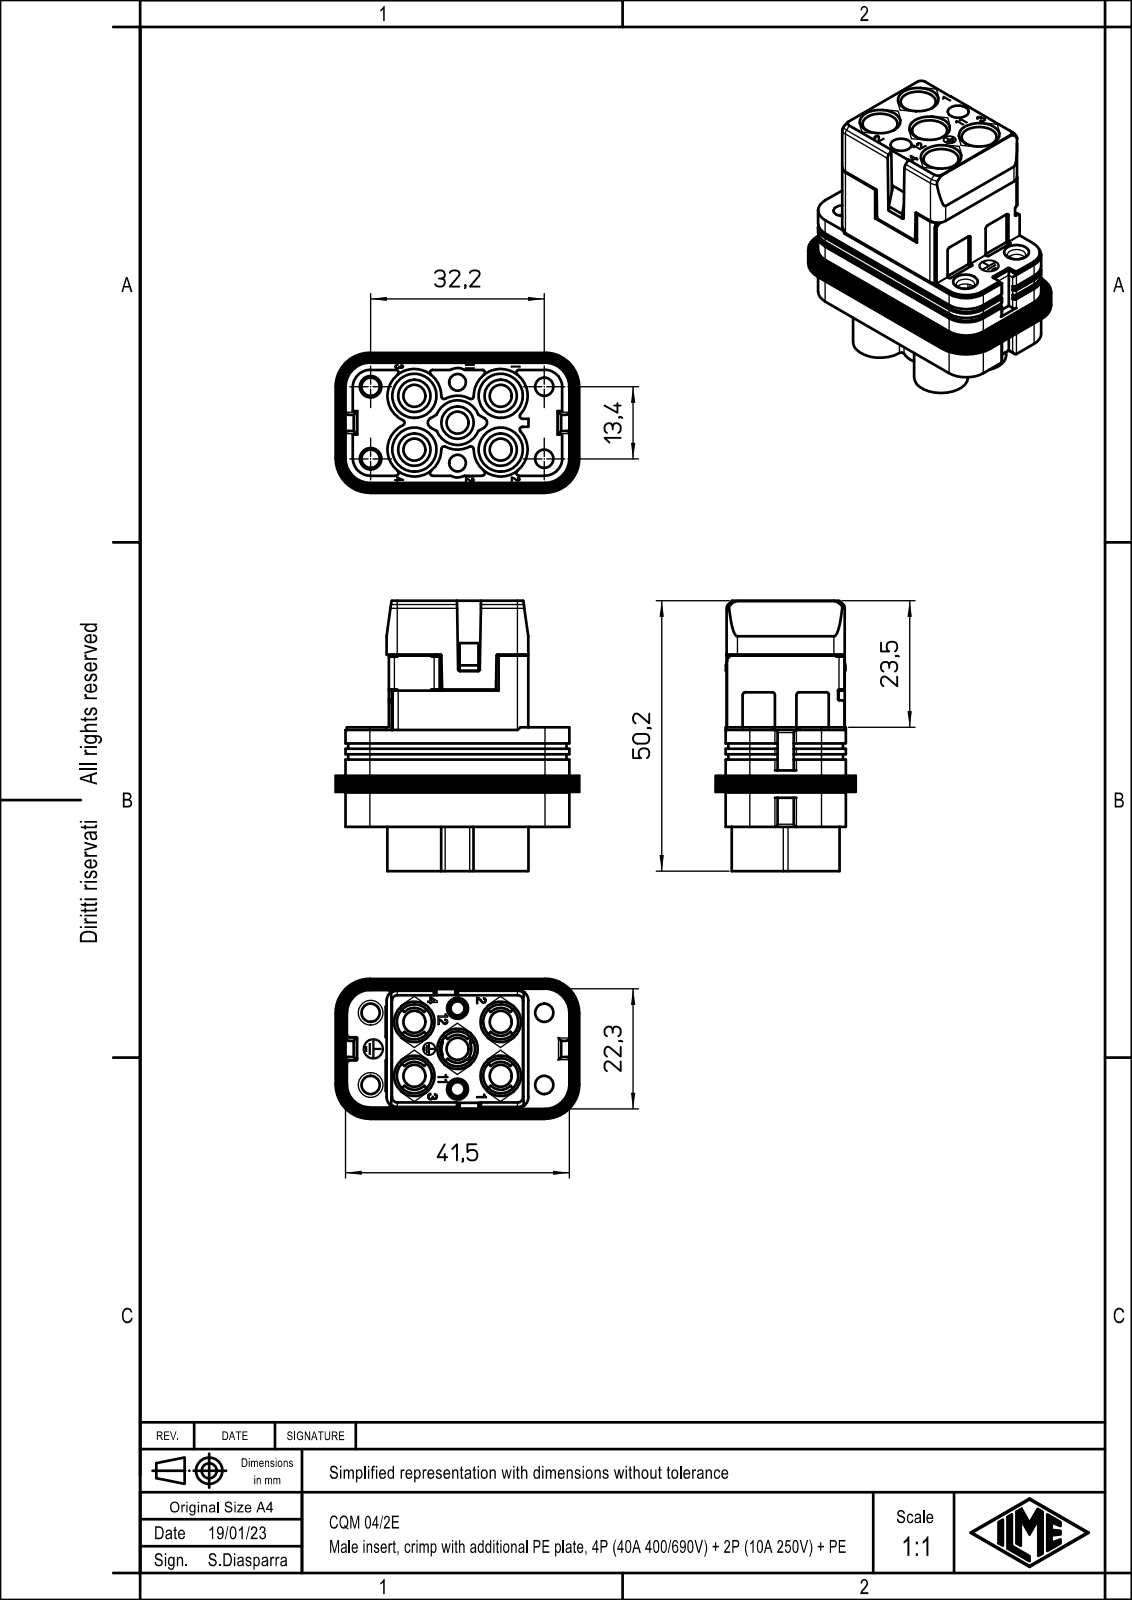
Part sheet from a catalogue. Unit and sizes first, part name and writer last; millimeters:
Units: millimetres
Overall size (bounding box): 50.2 × 45.2 × 26
Round holes (diameter × count): ⌀4.1 ×5, ⌀6.5 ×5, ⌀3.4 ×4, ⌀8.2 ×4, ⌀2.6 ×2, ⌀3.1 ×2, ⌀3.25 ×2, ⌀3.9 ×2, ⌀4 ×2
Round bosses / shafts (diameter × count): ⌀6 ×5
Partial cylindrical surfaces — rounded edges, fillets, slot ends (radius × count): R0.5 ×38, R1 ×16, R0.2 ×12, R5 ×5, R0.3 ×4, R2 ×4, R3.2 ×4, R4 ×4
Main face-to-face distances: 22.1, 1.33, 3, 20.77, 20.97, 1.13, 22.3, 0.5, 2, 21.9
Hole centre spacings: 8.28, 8.38, 9.43, 14.23, 14.84, 16.12, 17.44, 21.47
Volume: 16 901 mm³ · Surface area: 18 476 mm²
Bodies: 1 solid, 758 faces (487 planar, 211 cylindrical, 60 other)
Part name (STEP PRODUCT): CQM 04-2E
STEP written by: Creo Elements/Direct Modeling 20.1B 02-Apr-2019 (C) Parametric Technology GmbH (AUTOMOTIVE_DESIGN)
